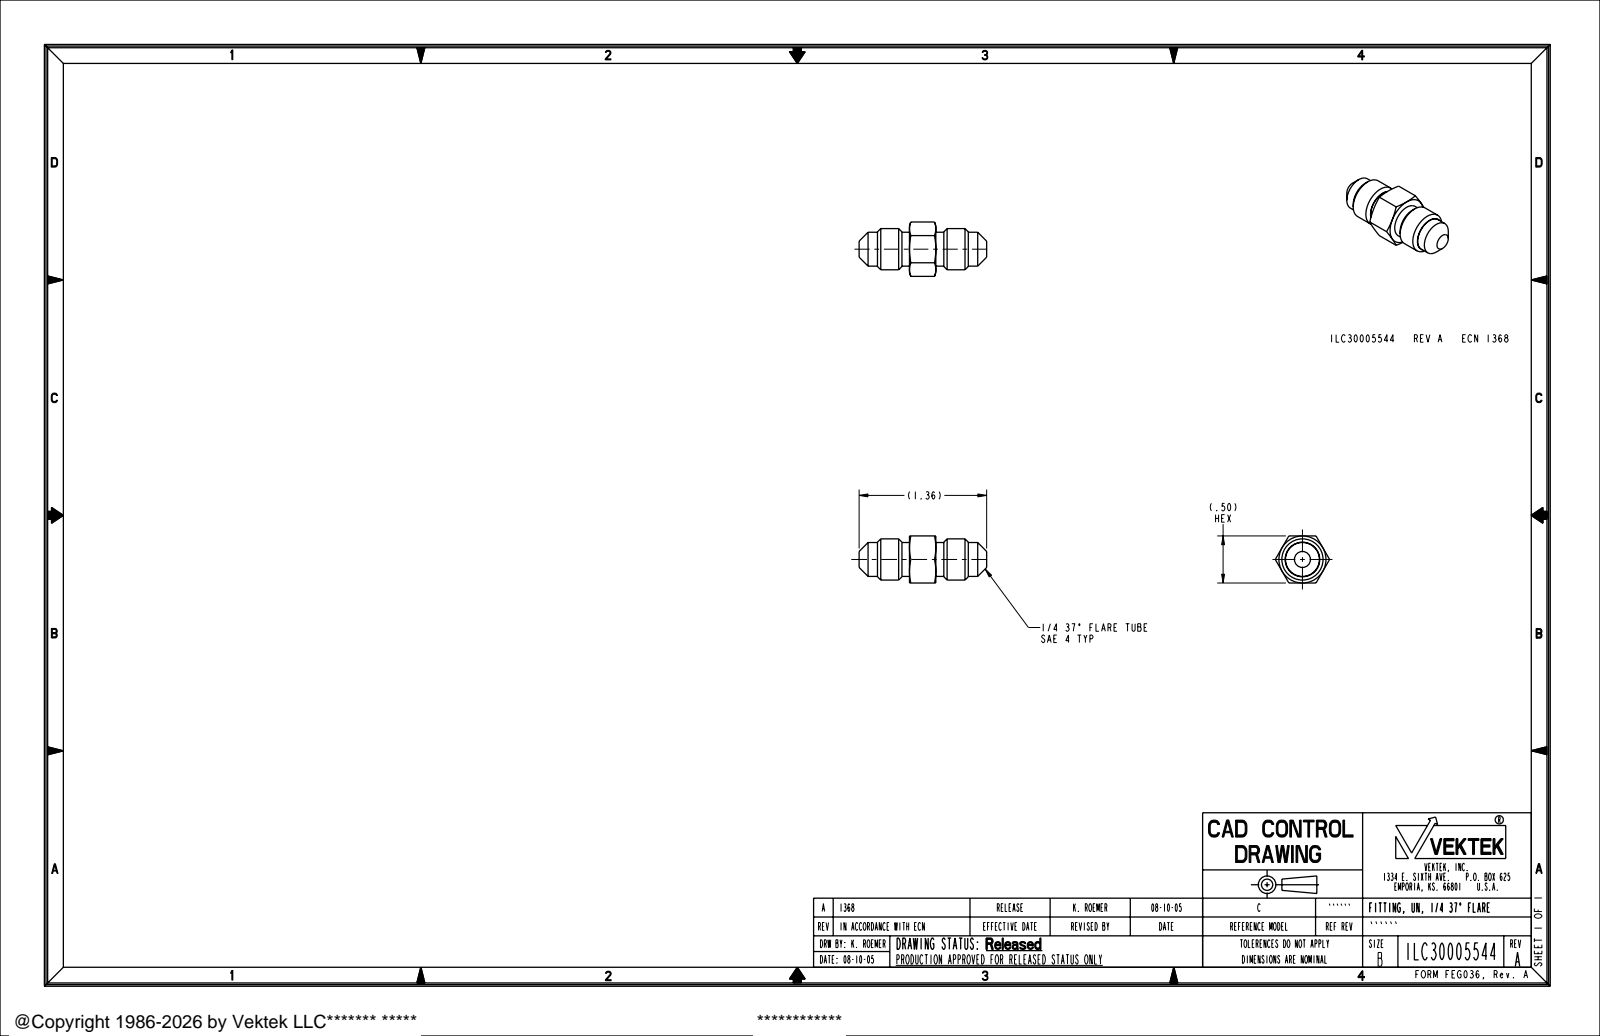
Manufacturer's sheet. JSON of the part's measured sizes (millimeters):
{"part_name": "ILC30005544", "step_written_by": "PRO/ENGINEER BY PARAMETRIC TECHNOLOGY CORPORATION, 2004290 (AUTOMOTIVE_DESIGN_CC2)", "units": "millimeters", "bodies": {"solids": 1, "faces": 50, "planar": 12, "cylindrical": 14, "other": 24}, "overall_size": [34.4, 14.7, 12.7], "volume_mm3": 2510, "surface_area_mm2": 1839, "round_holes": [[4.3, 1]], "round_bosses_or_shafts": [[11.1, 1], [9.1, 1]], "face_to_face_distances": [12.7, 7.1, 6.6, 17.9, 8.8, 15.9, 24.5, 2.2, 9.3, 11.3]}
